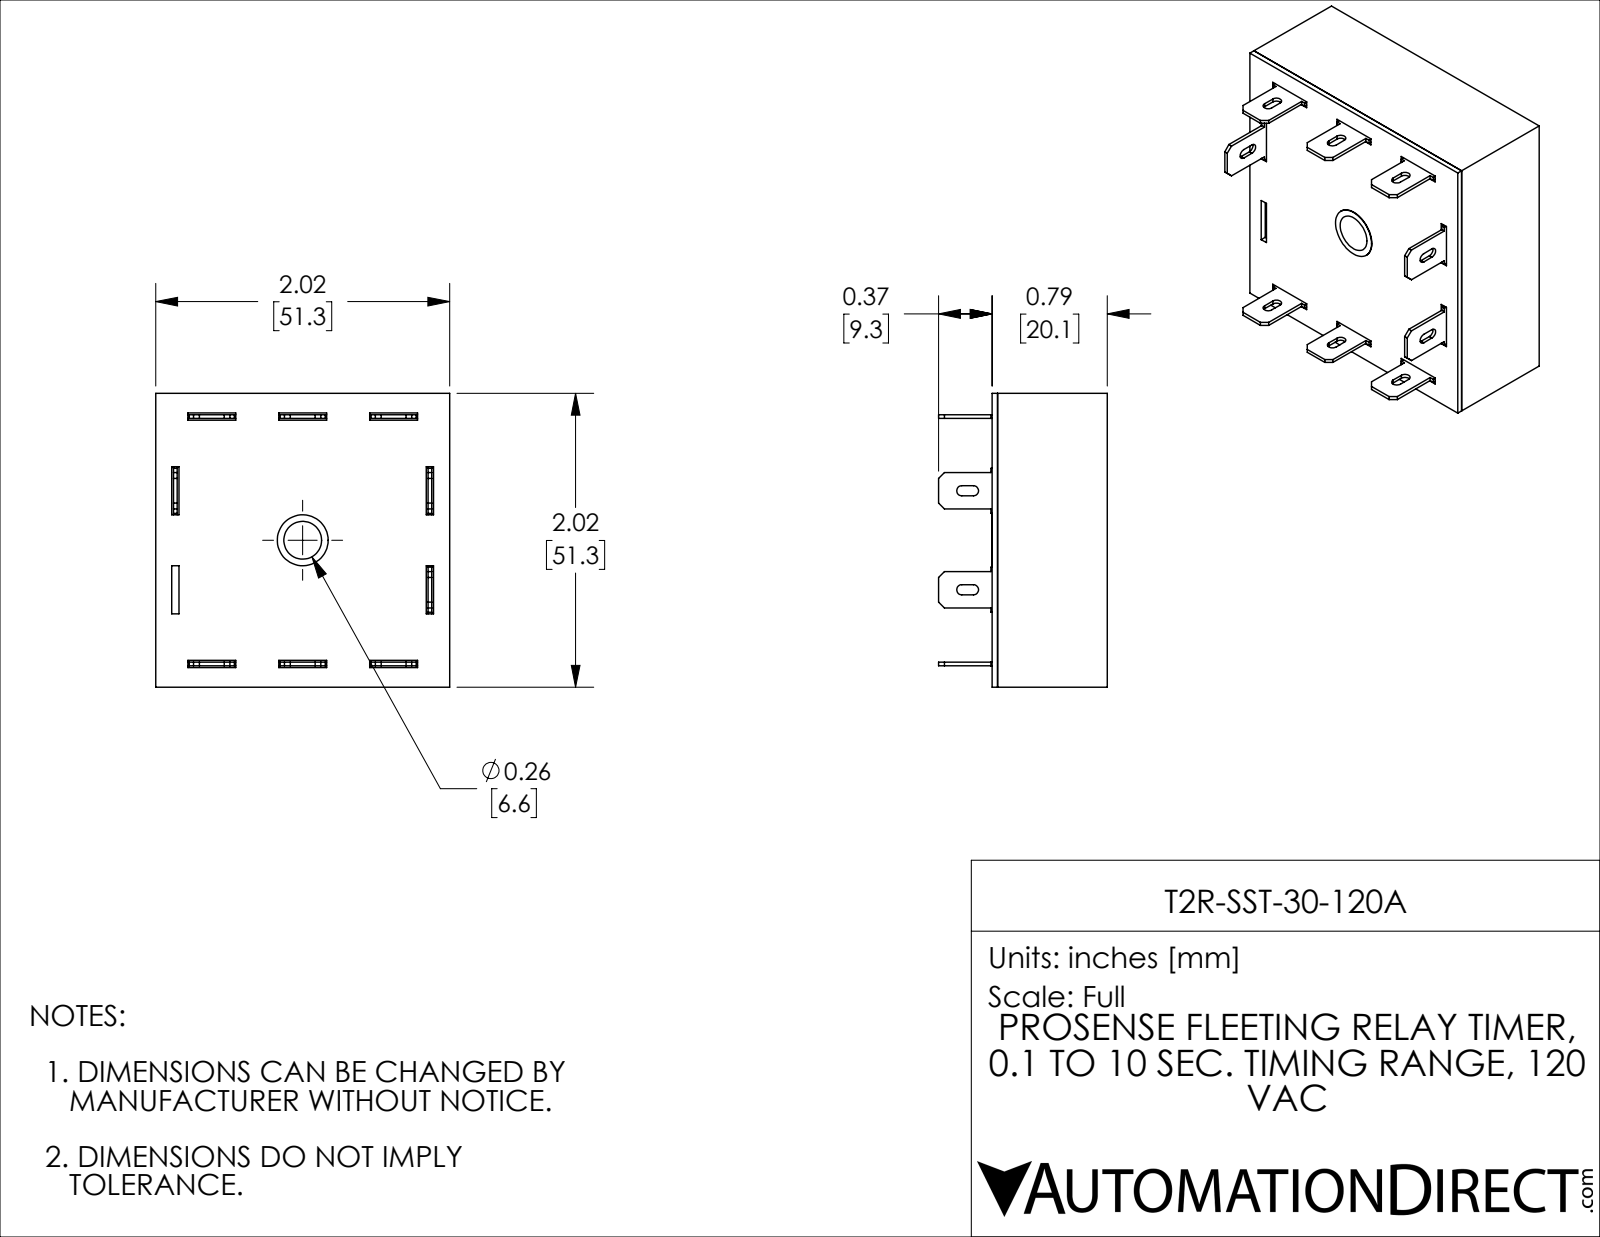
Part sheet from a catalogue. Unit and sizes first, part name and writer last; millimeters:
Units: millimetres
Overall size (bounding box): 51.31 × 51.31 × 29.46
Round holes (diameter × count): ⌀8.89 ×1
Partial cylindrical surfaces — rounded edges, fillets, slot ends (radius × count): R0.89 ×10
Main face-to-face distances: 1.14, 50.16, 19.15, 20.12, 0.97, 18.01, 18.98, 51.3, 3.74, 47.56
Volume: 11 178 mm³ · Surface area: 23 301 mm²
Bodies: 11 solids, 280 faces (256 planar, 22 cylindrical, 2 other)
Part name (STEP PRODUCT): T2R-SST-30-120A
STEP written by: SolidWorks 2021 (CONFIG_CONTROL_DESIGN)
